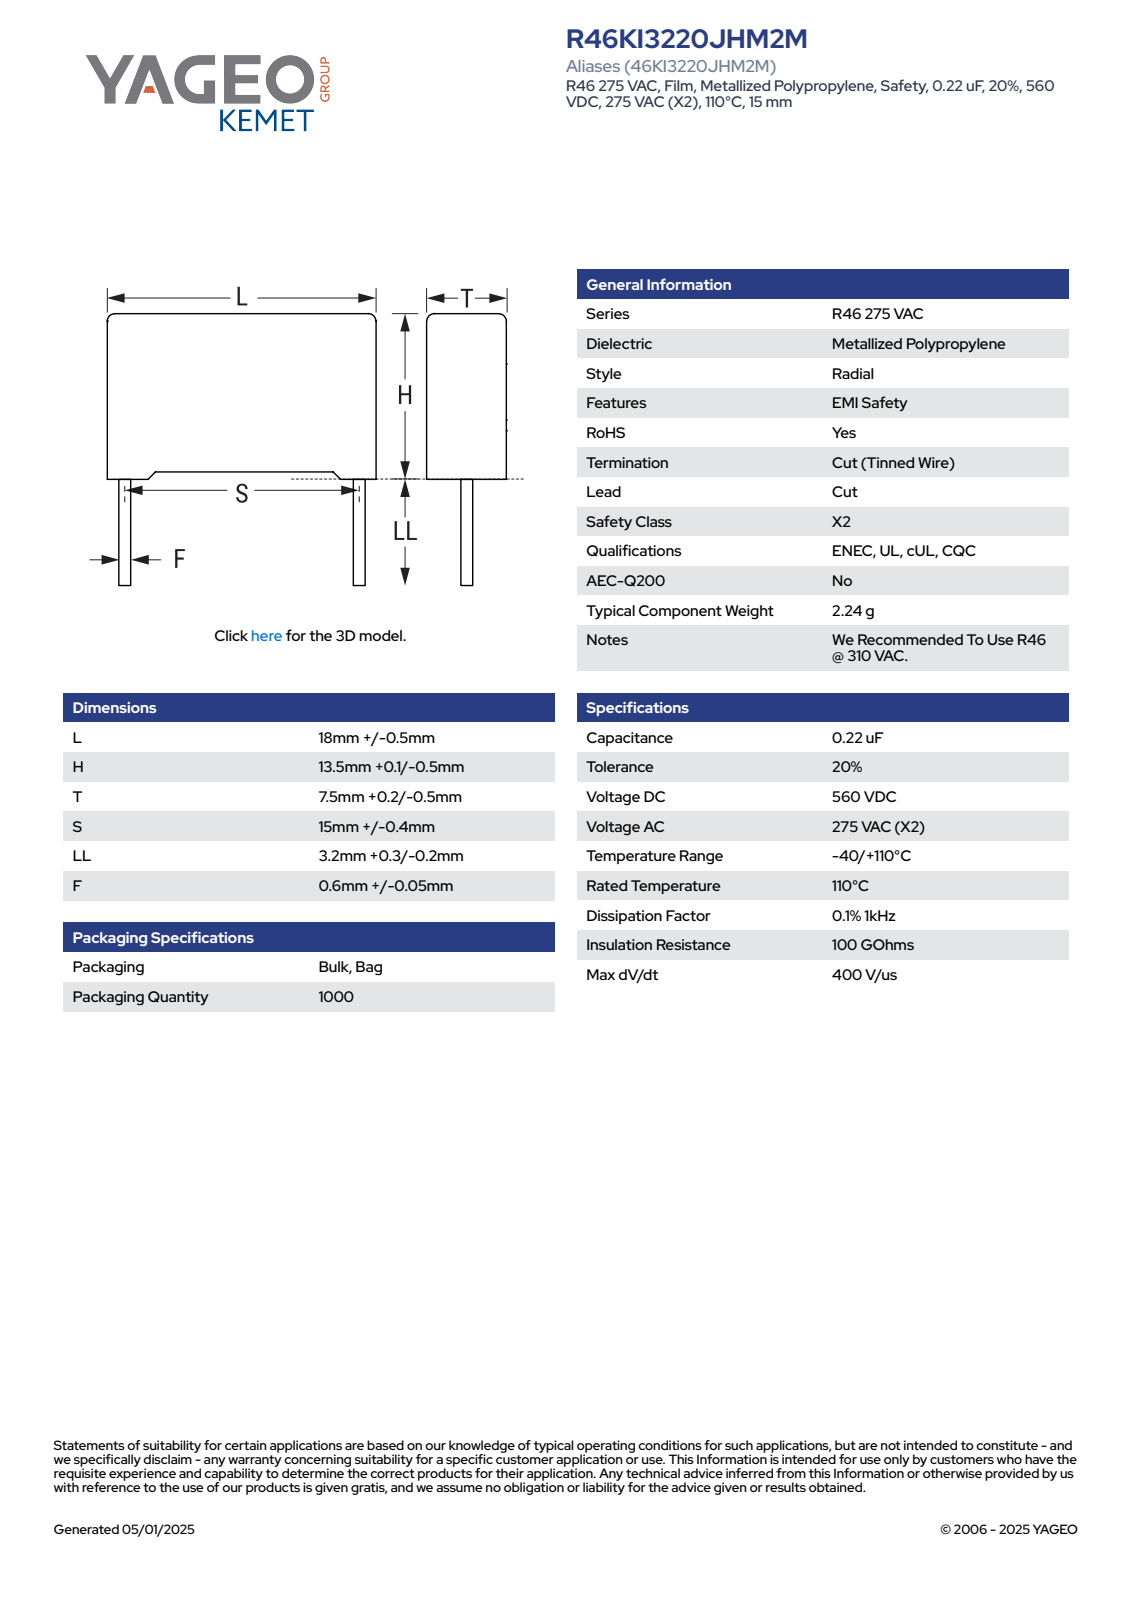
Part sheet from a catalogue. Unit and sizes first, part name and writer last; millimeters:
Units: millimetres
Overall size (bounding box): 18.5 × 17.1 × 7.71
Round bosses / shafts (diameter × count): ⌀0.65 ×2
Partial cylindrical surfaces — rounded edges, fillets, slot ends (radius × count): R0.5 ×4
Main face-to-face distances: 7.7, 12.85, 18.5, 0.62, 0.75, 13.6, 7.08, 0.47, 13.13, 17.88
Volume: 1 847 mm³ · Surface area: 1 044 mm²
Bodies: 4 solids, 85 faces (77 planar, 8 cylindrical, 0 other)
Part name (STEP PRODUCT): CFR_RB2_18X13.5X7.5_L18.5H13.6T7.7S15LL3.5F0.65
STEP written by: SolidWorks 2021 (AUTOMOTIVE_DESIGN)
